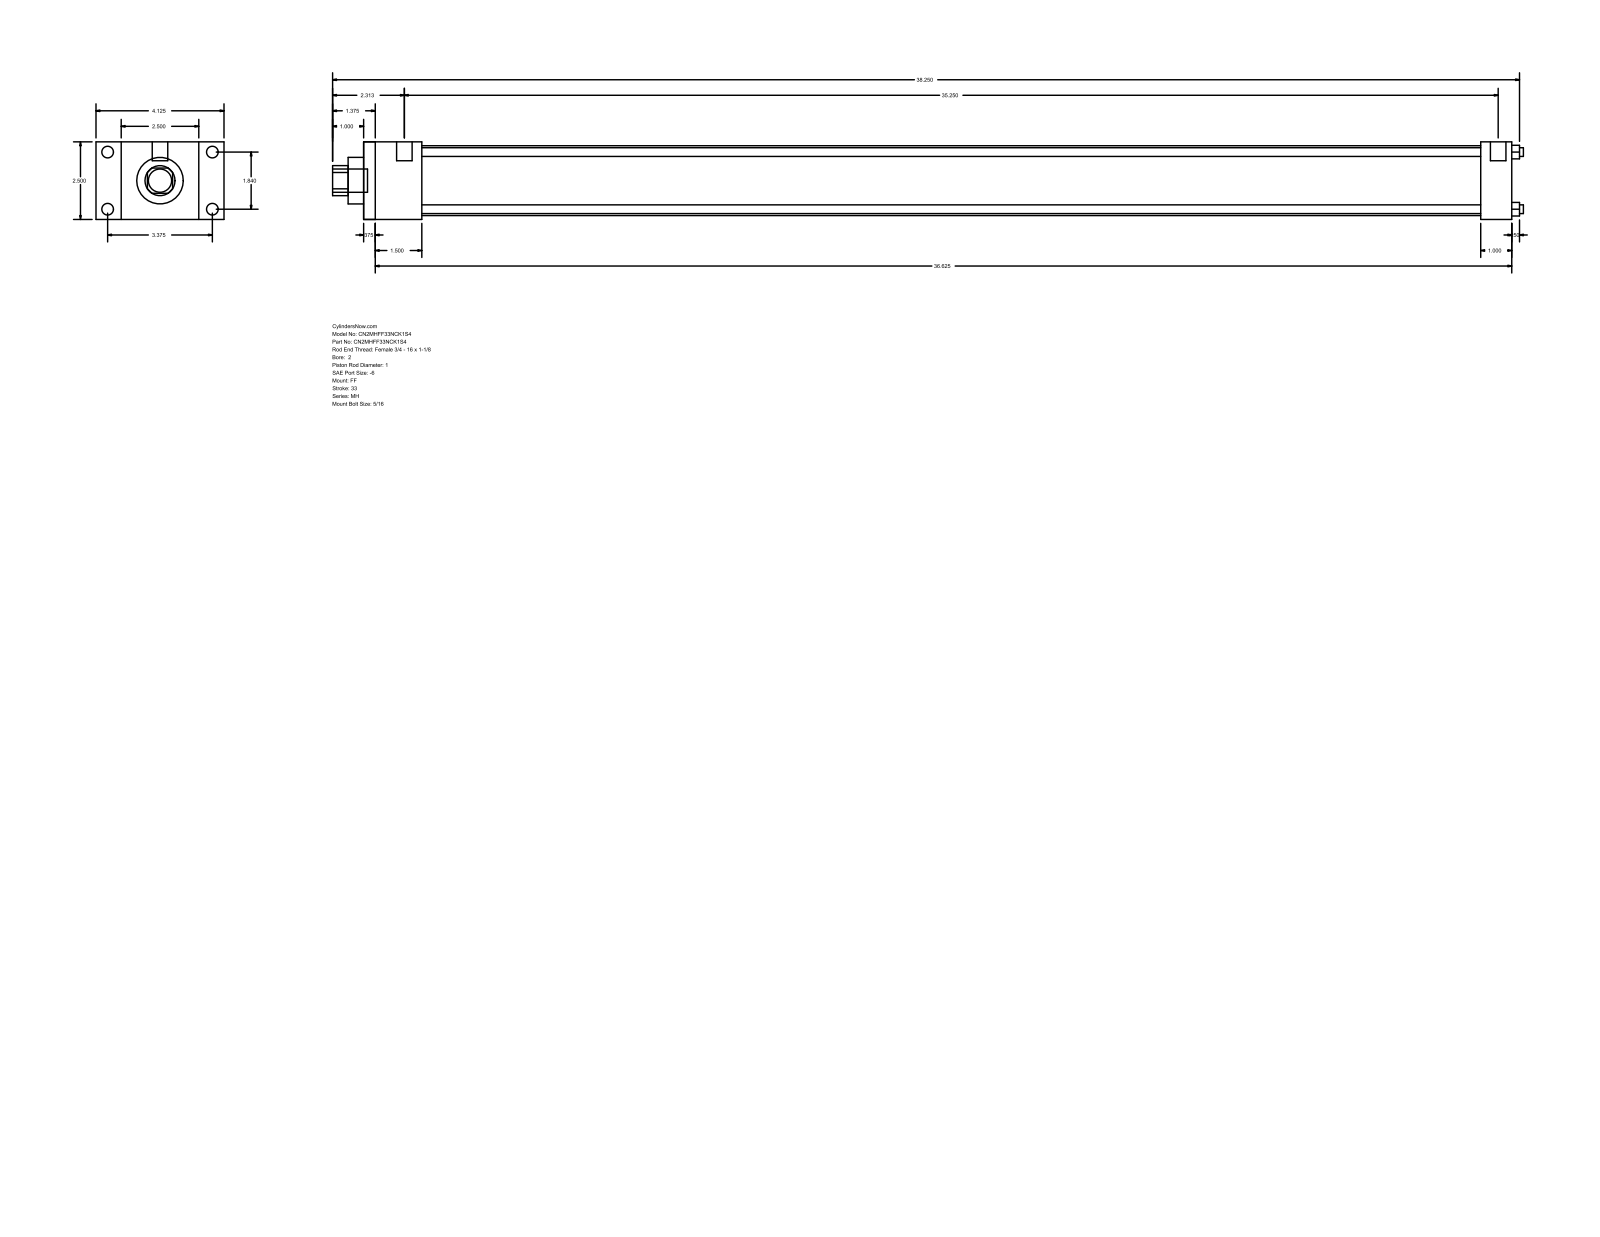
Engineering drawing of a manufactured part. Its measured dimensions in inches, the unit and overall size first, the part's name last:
Units: inches
Overall size (bounding box): 38.375 × 4.125 × 2.5
Round holes (diameter × count): ⌀0.281 ×4, ⌀1 ×1, ⌀1.5 ×1, ⌀2.25 ×1
Round bosses / shafts (diameter × count): ⌀0.375 ×4, ⌀0.219 ×4, ⌀0.5 ×2, ⌀0.75 ×1
Partial cylindrical surfaces — rounded edges, fillets, slot ends (radius × count): R0.484 ×1
Main face-to-face distances: 2.5, 37, 0.375, 36.625, 0.813, 1, 1.875, 36, 1.5, 35.625
Hole centre spacings: 1.301, 1.84, 2.602
Bodies: 0 solids, 92 faces (64 planar, 28 cylindrical, 0 other)
Part name (STEP PRODUCT): MH_FF__0200_1
STEP written by: GSSL Pune (CONFIG_CONTROL_DESIGN)
